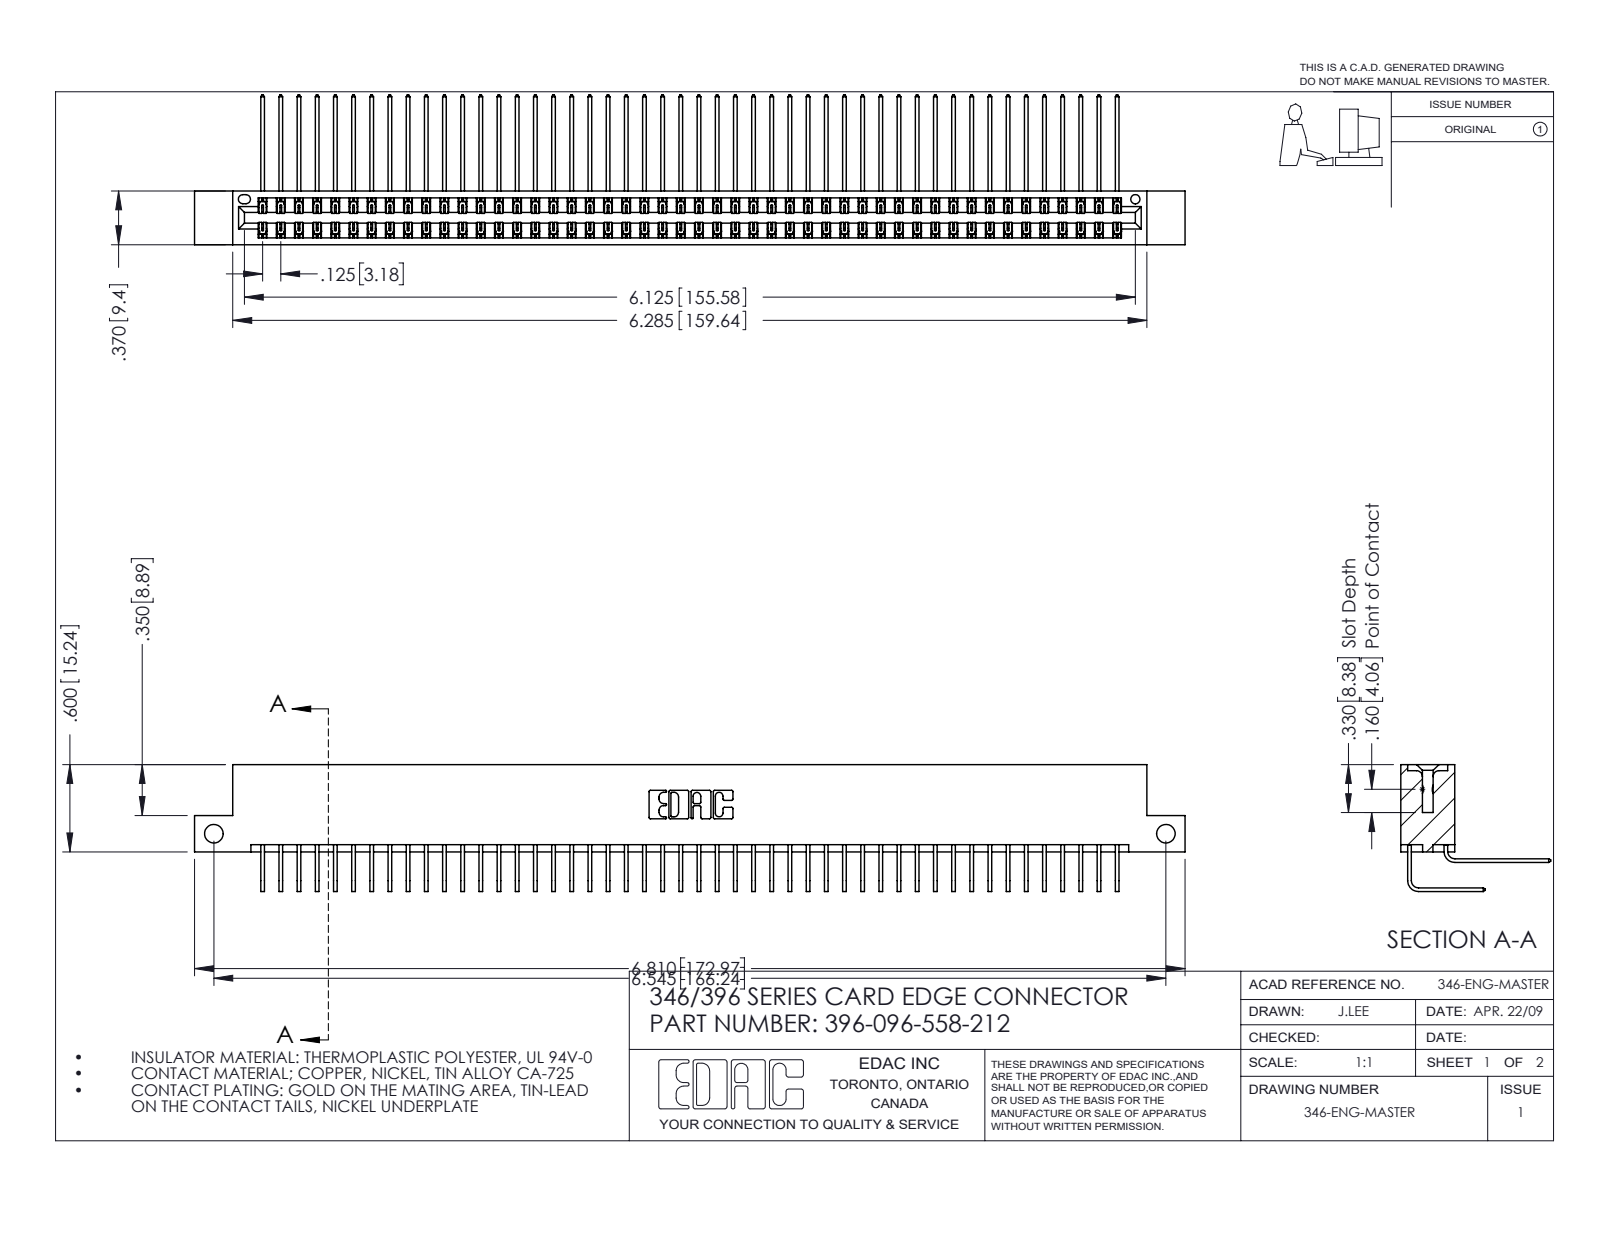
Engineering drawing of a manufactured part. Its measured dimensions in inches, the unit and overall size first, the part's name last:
Units: inches
Overall size (bounding box): 6.81 × 1.03 × 0.873
Round holes (diameter × count): ⌀0.128 ×2, ⌀0.064 ×1
Partial cylindrical surfaces — rounded edges, fillets, slot ends (radius × count): R0.006 ×144, R0.01 ×22, R0.007 ×6, R0.031 ×6, R0.026 ×3, R0.014 ×2, R0.022 ×2, R0.024 ×2
Main face-to-face distances: 0.322, 0.048, 0.025, 0.37, 0.25, 0.298, 0.072, 0.275, 0.148, 0.222
Hole centre spacings: 6.545
Volume: 1.061 in³ · Surface area: 41.08 in²
Bodies: 97 solids, 5306 faces (3628 planar, 1678 cylindrical, 0 other)
Part name (STEP PRODUCT): 345-292-001_558 Tail - 2; 345-292-001_558 559 Tail - 1; 346 Part_Flush Mounting Lugs - Side Mount; 396-096-558-212
STEP written by: SolidWorks 2016 (CONFIG_CONTROL_DESIGN)
